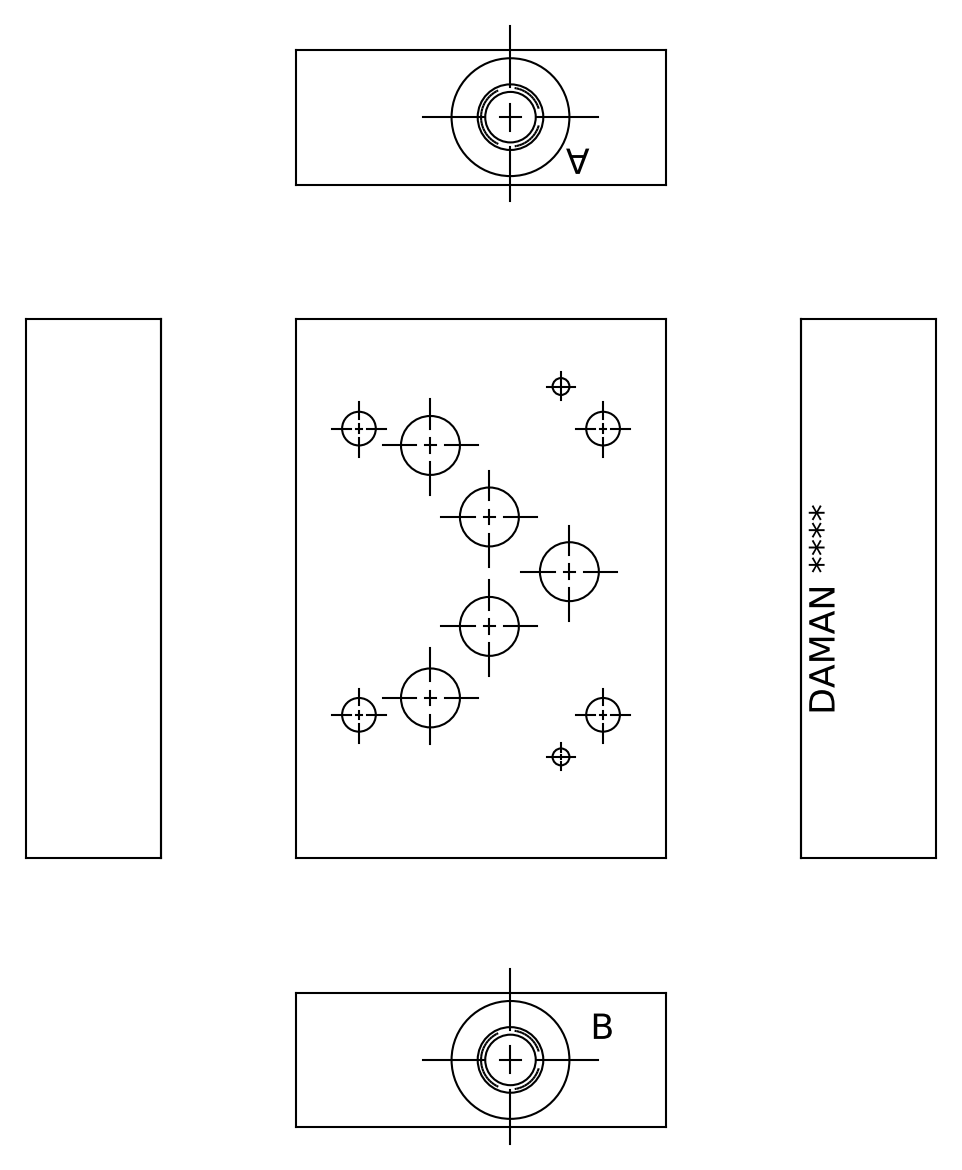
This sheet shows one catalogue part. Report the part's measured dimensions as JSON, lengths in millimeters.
{"part_name": "Part_AD05HETPAB4S.B00613R4_3D", "step_written_by": "Autodesk Inventor 2022 (AUTOMOTIVE_DESIGN)", "units": "millimeters", "bodies": {"solids": 1, "faces": 457, "planar": 309, "cylindrical": 37, "other": 111}, "overall_size": [101.6, 69.85, 25.4], "volume_mm3": 166635, "surface_area_mm2": 28104, "round_holes": [[11.11, 7], [15.88, 7], [7.14, 4], [11.13, 4], [3.17, 2], [9.53, 1], [9.88, 1], [12.4, 1], [21.29, 1]], "partial_cylinders_radius": [[3.57, 4]], "face_to_face_distances": [25.4, 69.85, 101.6, 24.08, 1.32, 0.79, 100.81, 100.02, 69.81, 12.29], "hole_center_spacings": [18.27, 47.63, 60.31, 17.48, 32.68, 35.4, 35.85, 3.15]}
